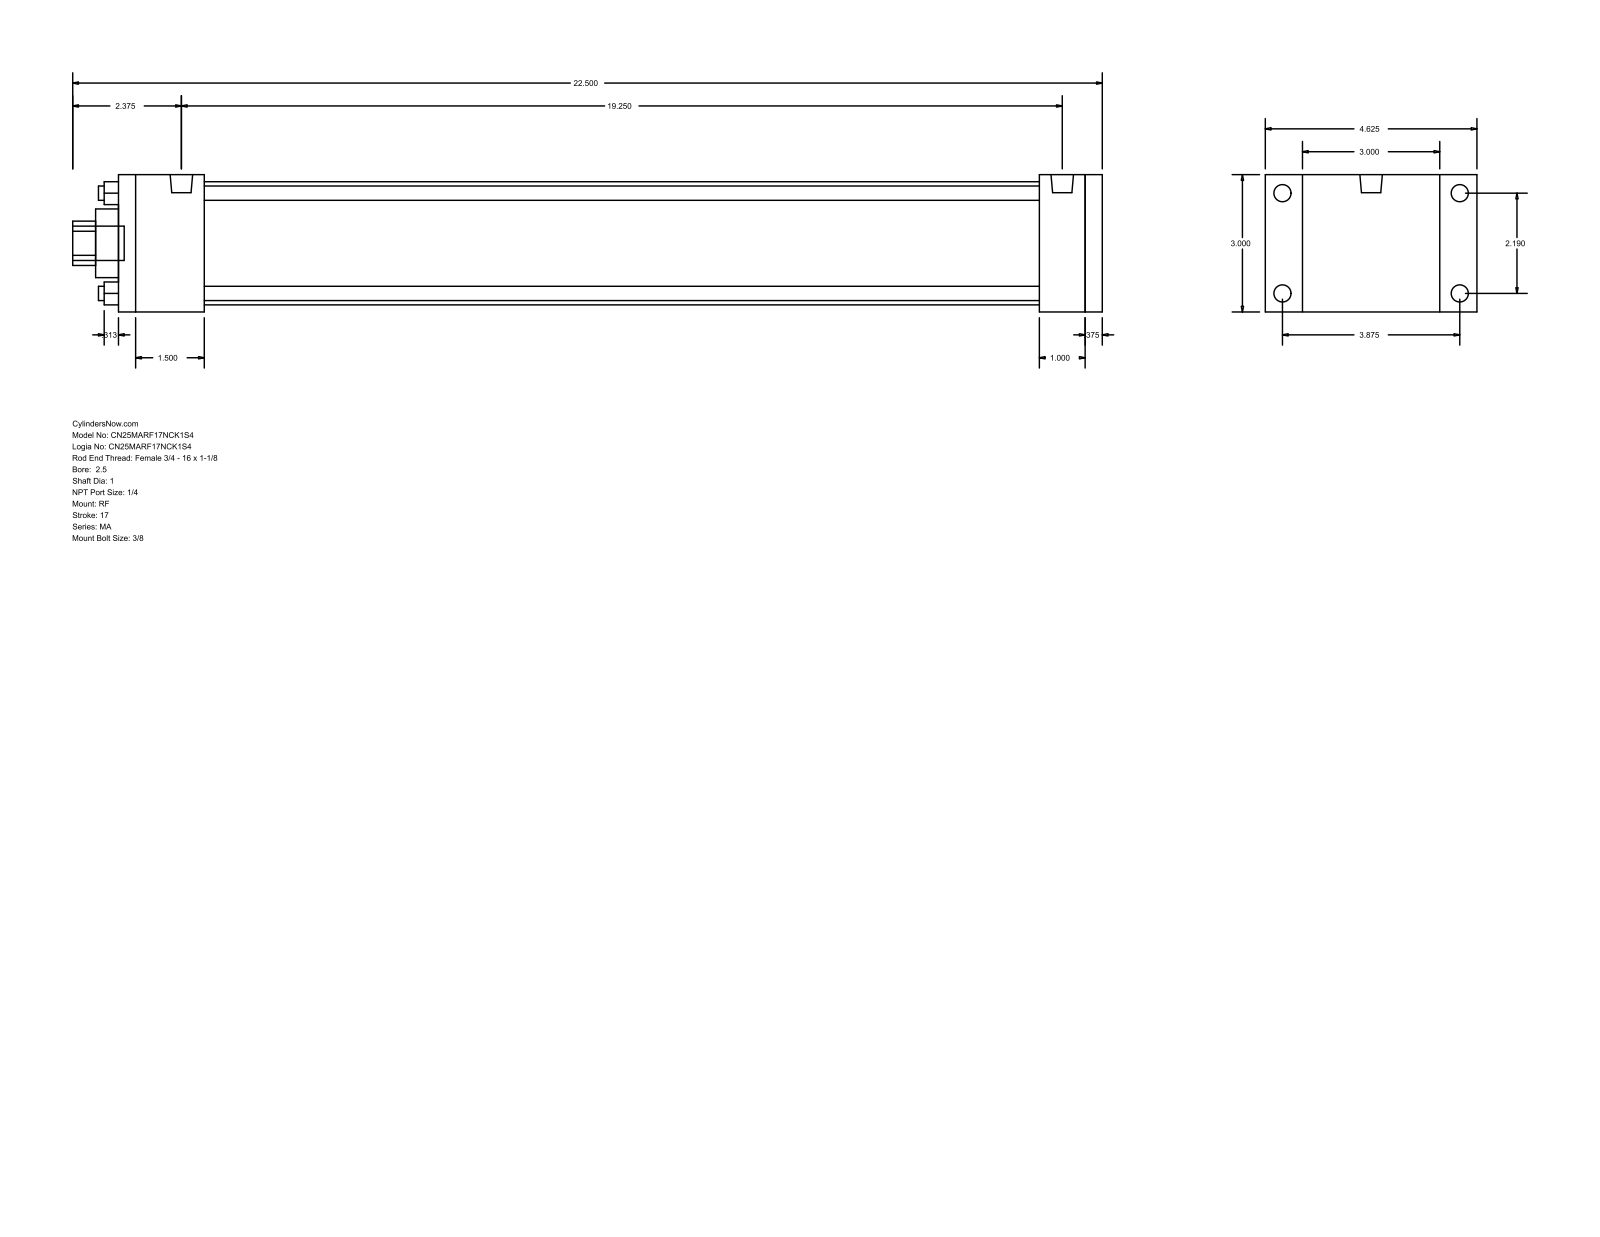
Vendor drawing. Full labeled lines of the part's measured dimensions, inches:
Part name (STEP PRODUCT): MA_RF__0250_1
STEP written by: GSSL Pune (CONFIG_CONTROL_DESIGN)
Units: inches
Bodies: 0 solids, 92 faces (64 planar, 28 cylindrical, 0 other)
Overall size (bounding box): 22.5 × 4.625 × 3
Round holes (diameter × count): ⌀0.313 ×4, ⌀1 ×1, ⌀1.5 ×1, ⌀2.69 ×1
Round bosses / shafts (diameter × count): ⌀0.375 ×4, ⌀0.313 ×4, ⌀0.492 ×2, ⌀0.75 ×1
Partial cylindrical surfaces — rounded edges, fillets, slot ends (radius × count): R0.484 ×1
Main face-to-face distances: 3, 21.5, 21.125, 0.375, 1, 1.875, 20.125, 18.25, 19.25, 19.625
Hole centre spacings: 1.548, 2.19, 3.097
